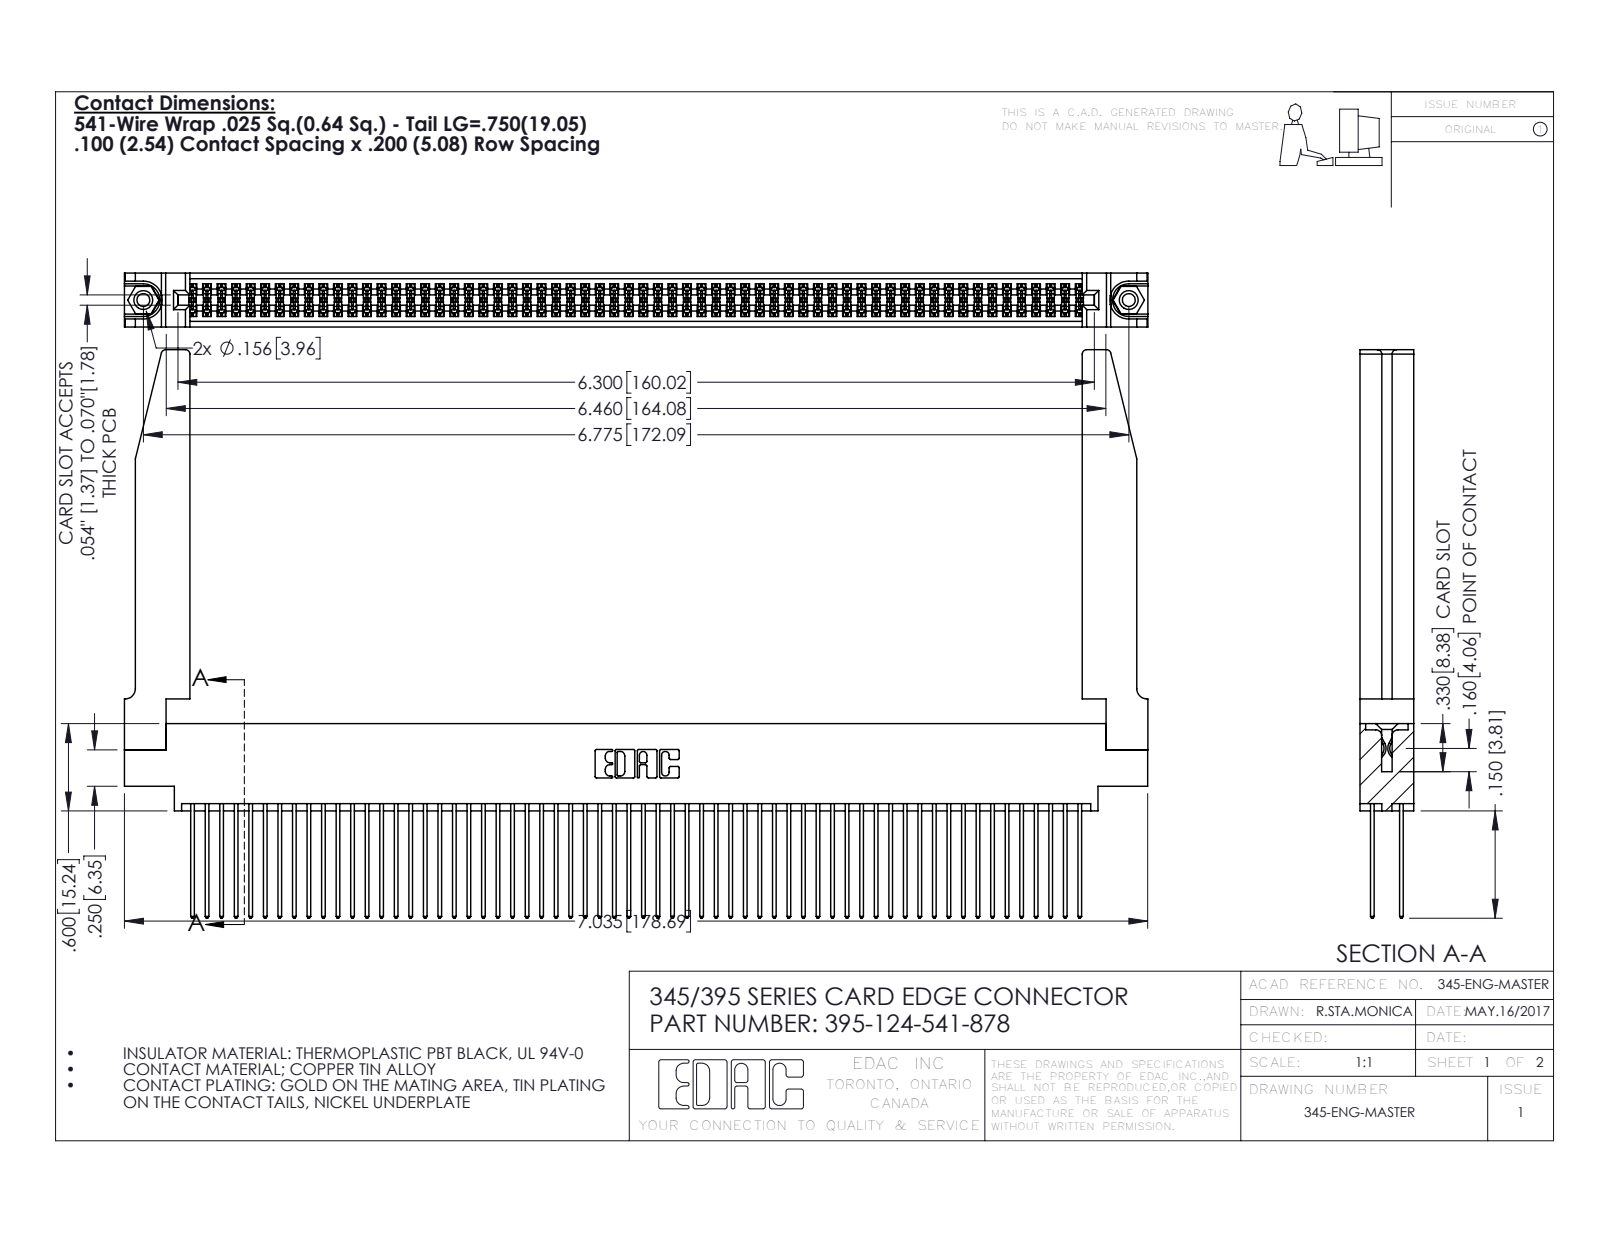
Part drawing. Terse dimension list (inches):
name: 345-250-001_345-250-001-102; 345 Part_0.170 Offset - 0.156 Dia-TH; 395-124-541-878; 345-220-078_345-220-078 (+1 more)
written by: SolidWorks 2016 (CONFIG_CONTROL_DESIGN)
unit: in
bodies: 129 solids, 6564 faces (4318 planar, 2194 cylindrical, 52 other)
size: 7.036 × 3.907 × 0.37
volume: 1.581 in³; area: 58.18 in²
holes: 2× ⌀0.089, 2× ⌀0.125, 2× ⌀0.156, 1× ⌀0.064
bosses: 2× ⌀0.155
rounds: 186× R0.006, 124× R0.01, 22× R0.01, 8× R0.03, 6× R0.007, 6× R0.031, 3× R0.026, 2× R0.014
face distances: 0.072, 0.298, 0.37, 0.098, 0.272, 0.025, 0.2, 0.225, 0.175, 0.148
hole spacings: 0.27, 6.539, 6.775
